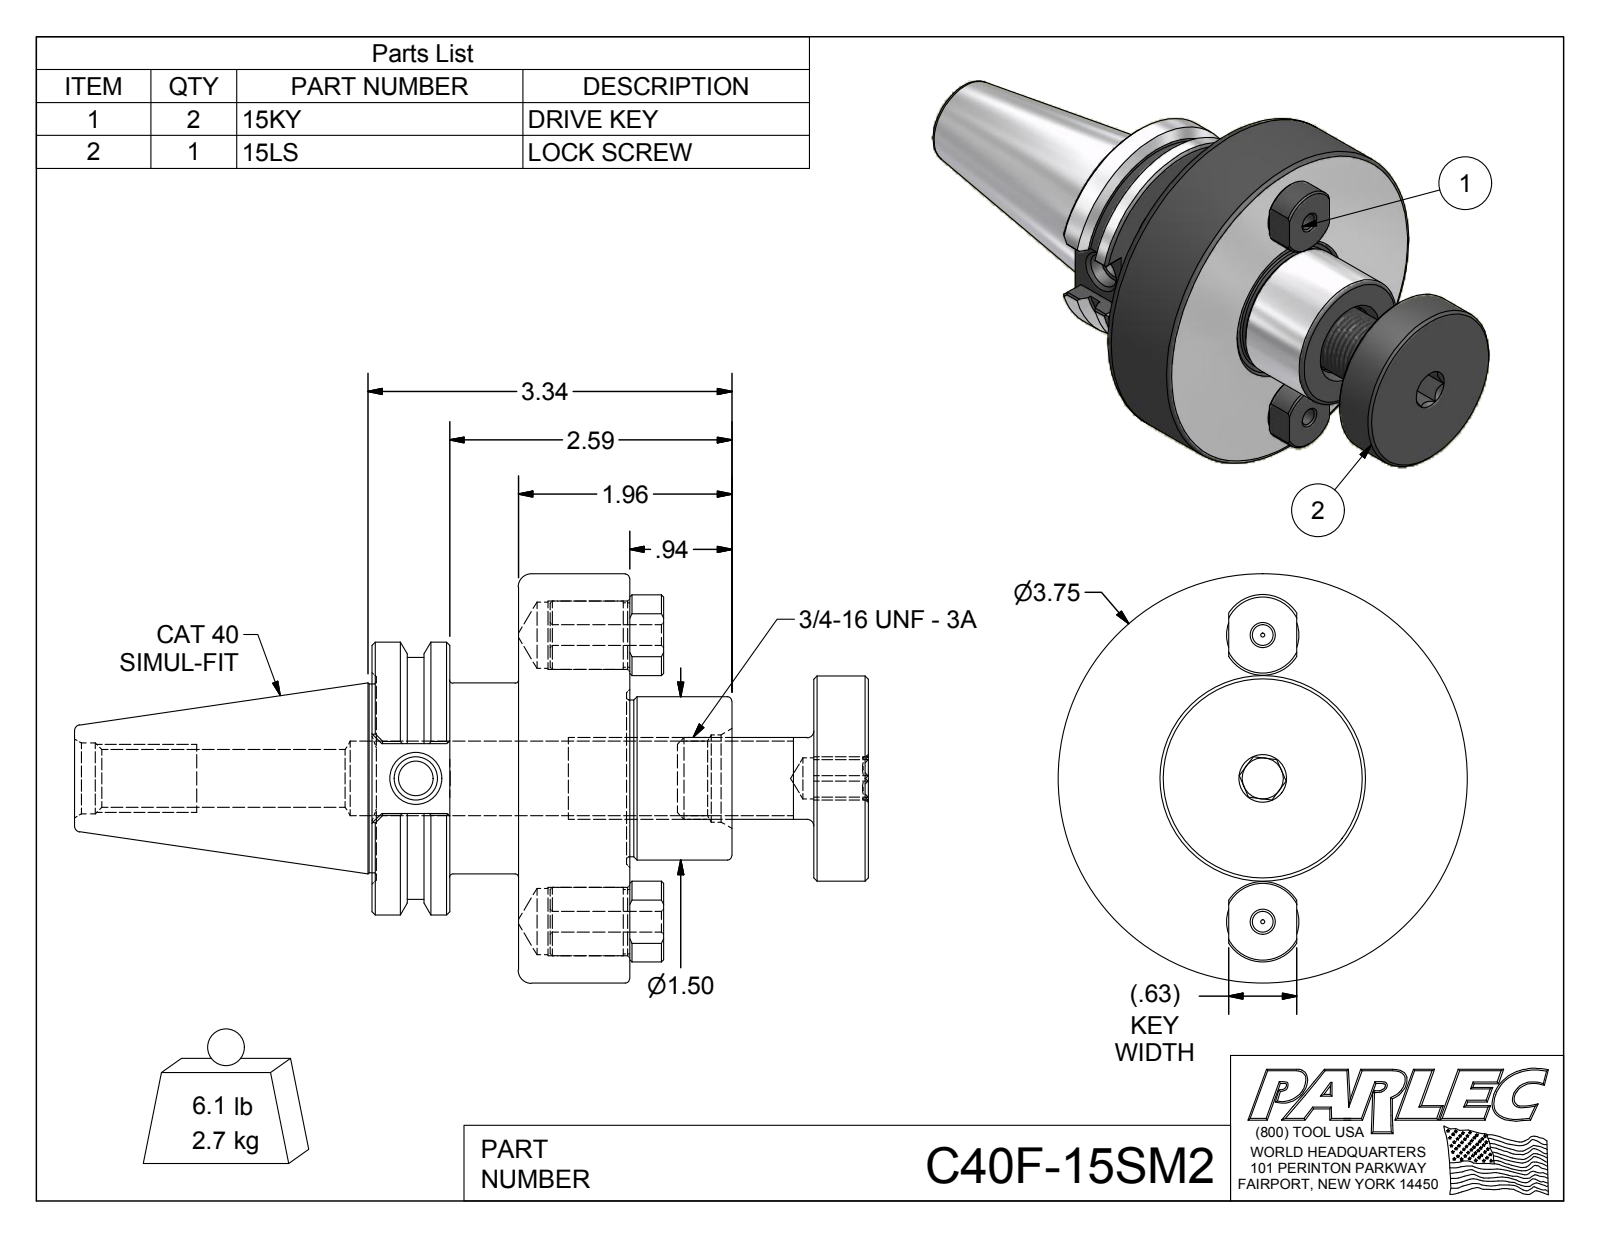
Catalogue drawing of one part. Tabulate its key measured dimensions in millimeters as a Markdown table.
| quantity | value |
| --- | --- |
| part name | C40F-15SM2; C40F-15SM2-1; 15KY; 15LS |
| STEP written by | Autodesk Inventor 2012 (AUTOMOTIVE_DESIGN) |
| units | millimeters |
| bodies | 4 solids, 154 faces (64 planar, 34 cylindrical, 56 other) |
| overall size | 184.8 × 95.3 × 95.3 |
| volume | 352 000 mm³ |
| surface area | 62 210 mm² |
| round holes (diameter × count) | 4.8 × 2, 15.3 × 2, 15.8 × 2, 8 × 1, 9.5 × 1, 10.1 × 1, 13.4 × 1, 16.5 × 1, 17.3 × 1, 20.3 × 1 |
| round bosses / shafts (diameter × count) | 15.9 × 2, 15 × 2, 95.3 × 1, 63.5 × 1, 56.3 × 1, 47.8 × 1, 44.5 × 1, 43.9 × 1 |
| partial cylindrical surfaces (radius × count) | 9.4 × 2 |
| main face-to-face distances | 25.9, 81.5, 55.5, 12.7, 42.8, 68.8, 16, 41.9, 84.8, 97.5 |
| hole center spacings | 33.3, 66.6 |
